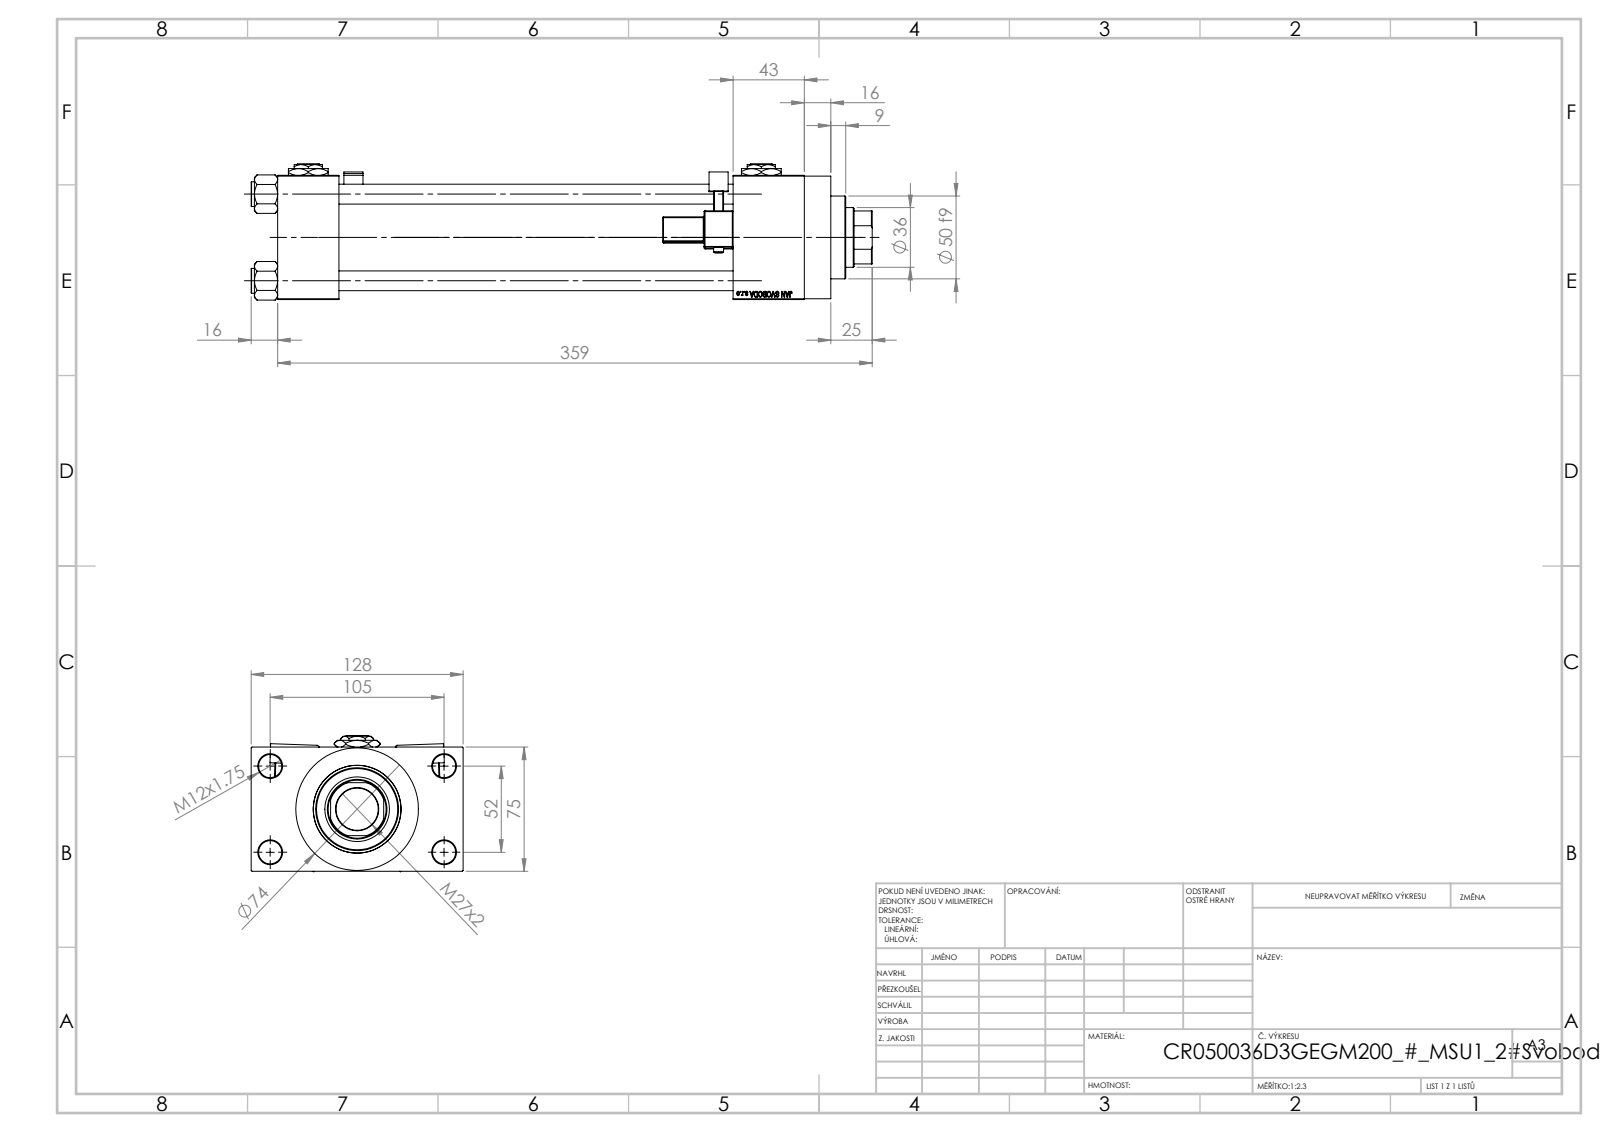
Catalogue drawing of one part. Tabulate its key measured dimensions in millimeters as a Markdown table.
| quantity | value |
| --- | --- |
| part name | V215CR_MSU; V215CR_VCP_D; V215CR_D_Body; Zatka_pro_OIL_PORT (+3 more) |
| STEP written by | SolidWorks 2019 (CONFIG_CONTROL_DESIGN) |
| units | millimeters |
| bodies | 15 solids, 1359 faces (603 planar, 160 cylindrical, 596 other) |
| overall size | 375 × 128 × 82.27 |
| volume | 1 218 000 mm³ |
| surface area | 297 739 mm² |
| round holes (diameter × count) | 12 × 4, 14 × 4, 7 × 2, 20.96 × 2, 30 × 2, 25.5 × 1, 36 × 1, 39 × 1, 41 × 1, 53 × 1 |
| round bosses / shafts (diameter × count) | 15 × 4, 6 × 2, 74 × 1, 56 × 1, 50 × 1 |
| partial cylindrical surfaces (radius × count) | 0.5 × 48, 1 × 2, 2.5 × 2, 4 × 2, 17.5 × 1 |
| main face-to-face distances | 75, 238, 101.5, 37, 275, 26.5, 43, 318, 281, 16 |
| hole center spacings | 26.35, 36.98, 52.3, 58.43, 58.59, 78.65, 94.37, 52 |
